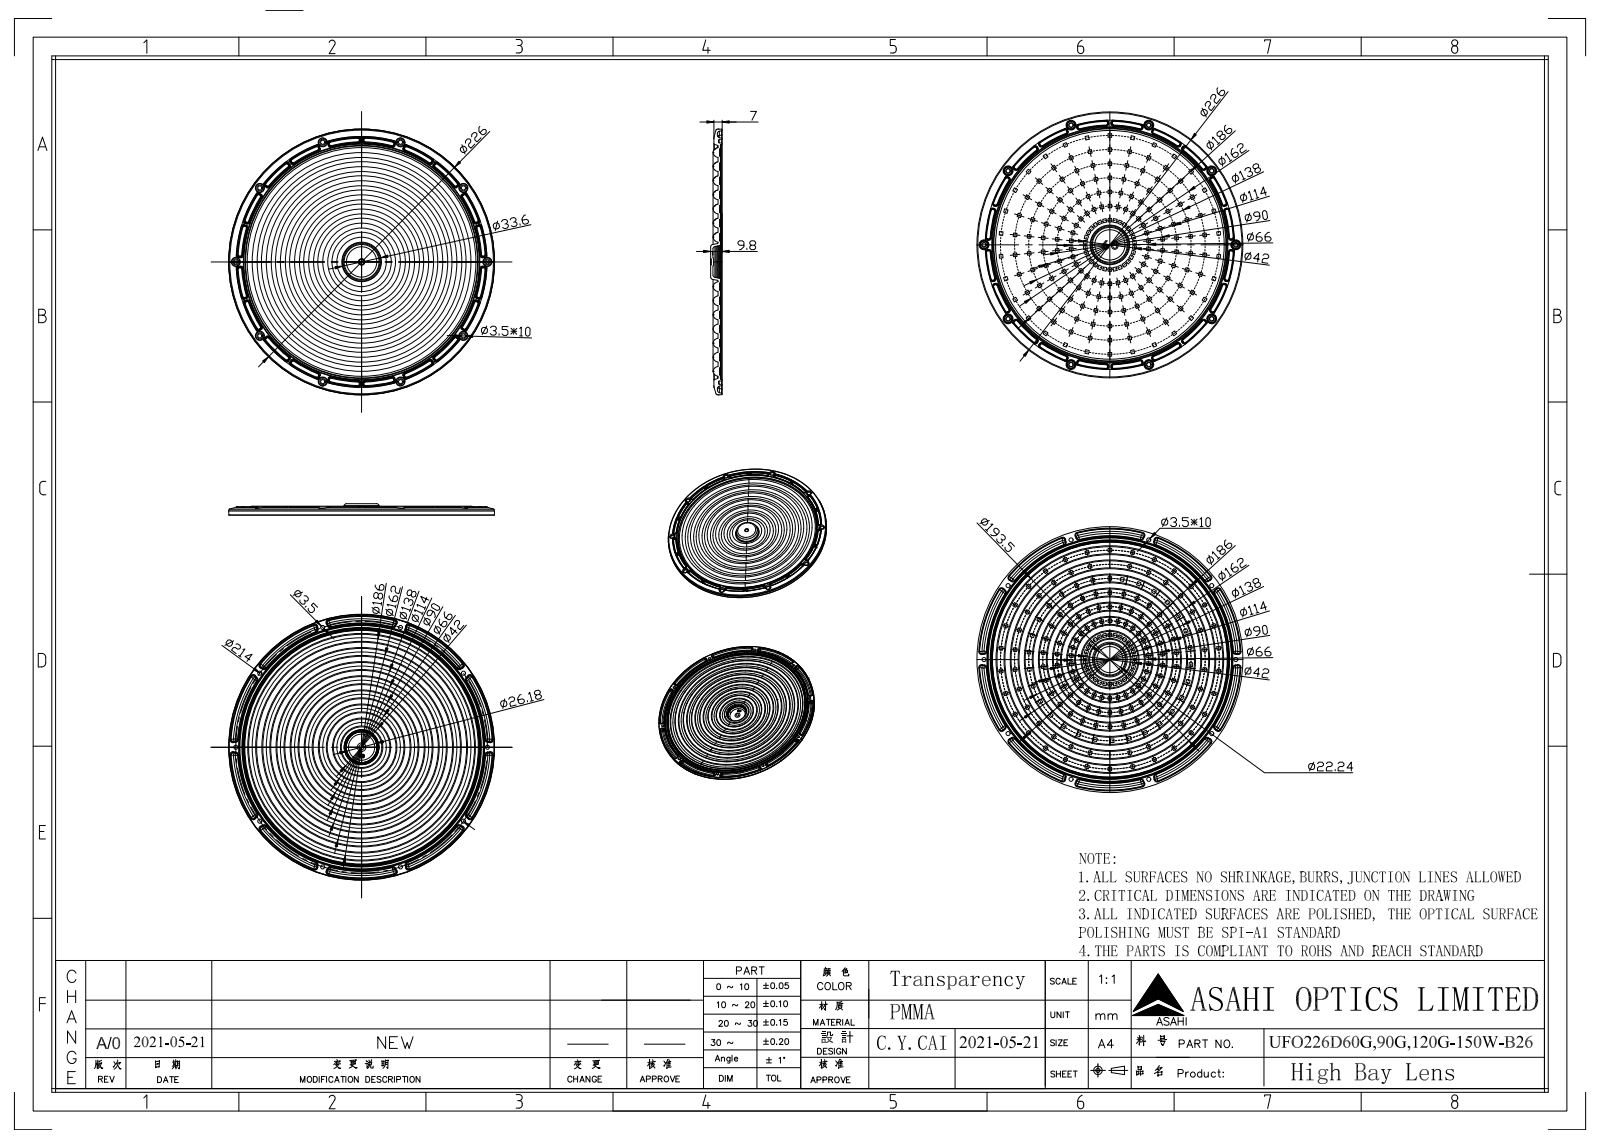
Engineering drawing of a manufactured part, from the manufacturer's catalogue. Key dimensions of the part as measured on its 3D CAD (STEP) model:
Part name (STEP PRODUCT): L353-4_UFO226-T90-B26-KH
STEP written by: SolidWorks 2019 (AUTOMOTIVE_DESIGN)
Units: millimetres
Bodies: 1 solid, 1008 faces (118 planar, 82 cylindrical, 808 other)
Overall size (bounding box): 226 × 226 × 9.8
Volume: 128 167 mm³ · Surface area: 102 416 mm²
Round holes (diameter × count): ⌀5 ×1
Partial cylindrical surfaces — rounded edges, fillets, slot ends (radius × count): R0.5 ×74
Main face-to-face distances: 0.7, 2, 1.3, 3, 1.5, 2.2, 0.5, 3.5, 3.7, 1.7
